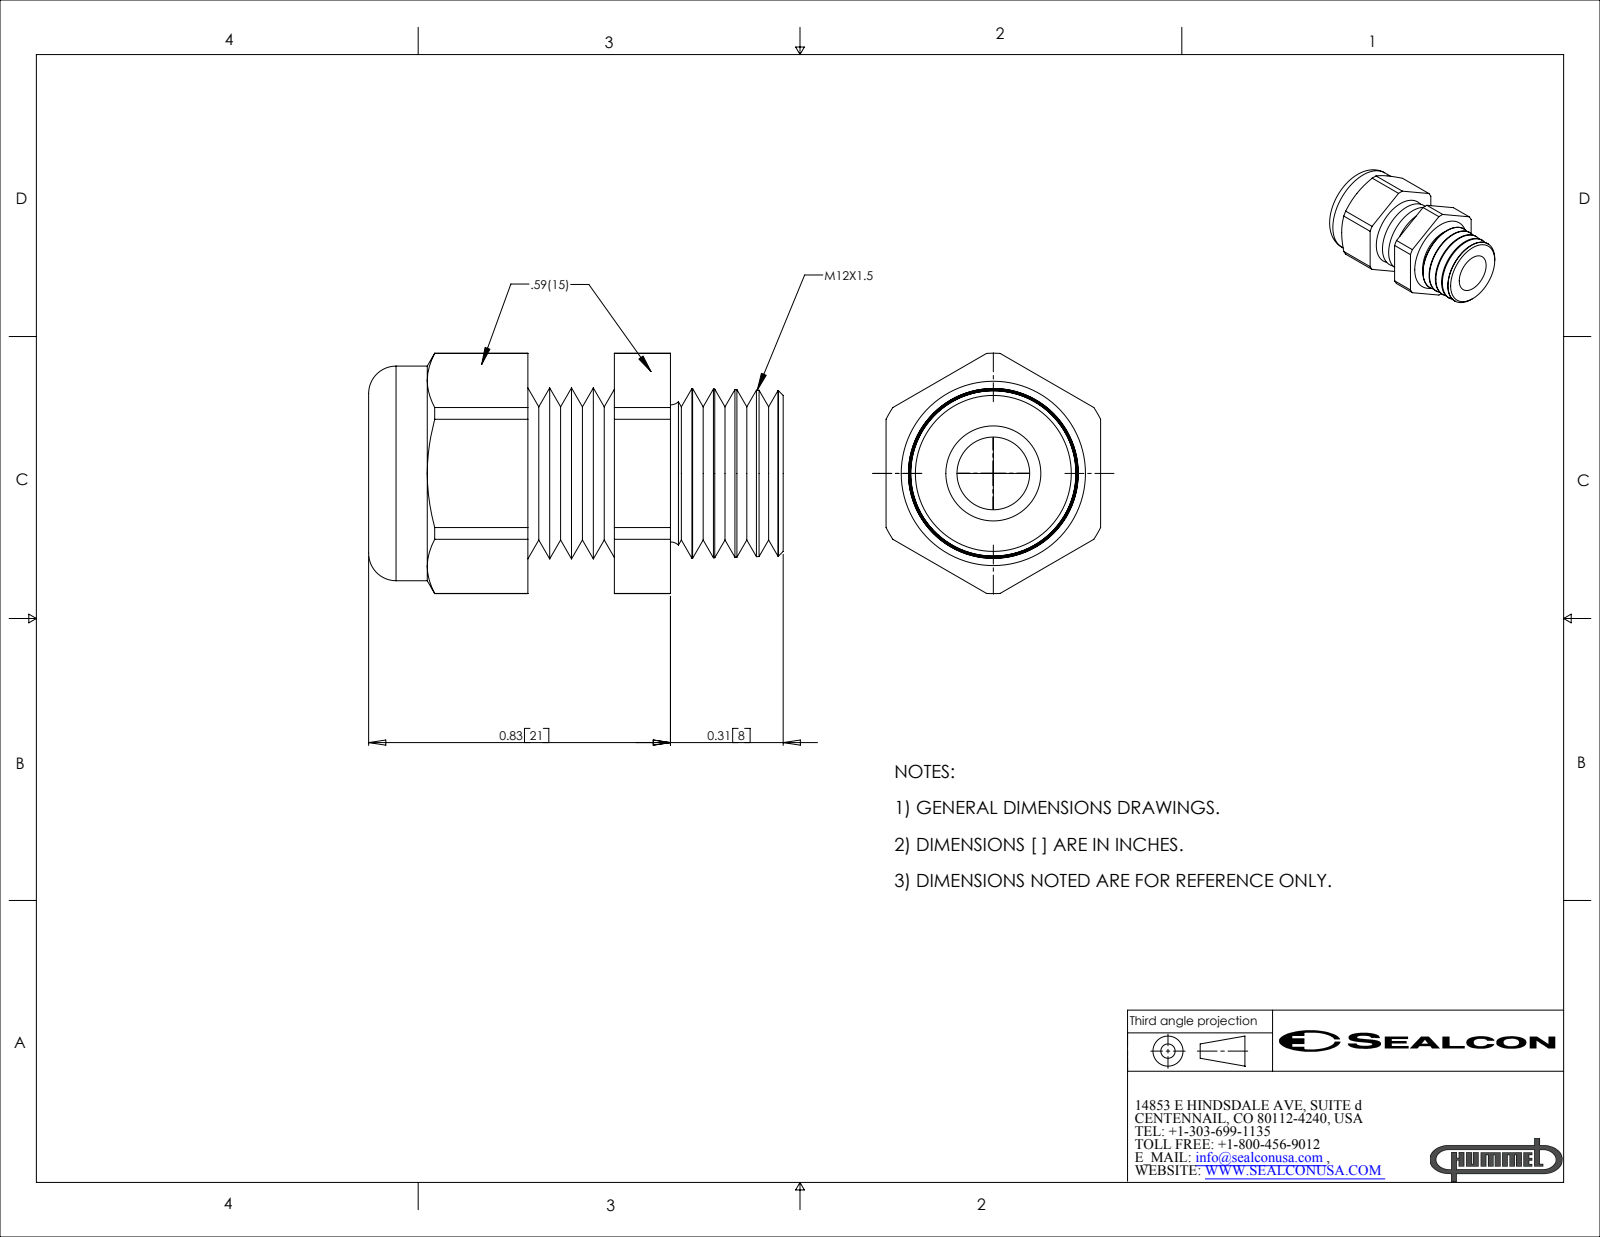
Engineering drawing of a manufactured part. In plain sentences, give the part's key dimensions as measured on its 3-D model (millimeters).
The part is named "CD12MR-GY". Its 3-D file was written by "SolidWorks 2007 (CONFIG_CONTROL_DESIGN)". It is 2 solids with 108 faces: 20 planar, 24 cylindrical and 64 other. Overall it measures 29 by 16.8 by 15 millimeters. Its volume is 3 240 cubic millimeters and its surface area 2 992 square millimeters. Round holes: 1 of diameter 5.1, 1 of diameter 10.2, 1 of diameter 11.9. Round bosses or shafts: 1 of diameter 15. Partial cylindrical surfaces (rounded edges, fillets, slot ends): 1 of radius 8.4. The main face-to-face distances are 15, 13.1, 7, 6, 17, 10, 3.9, 24.9, 17.8, 11.8.
